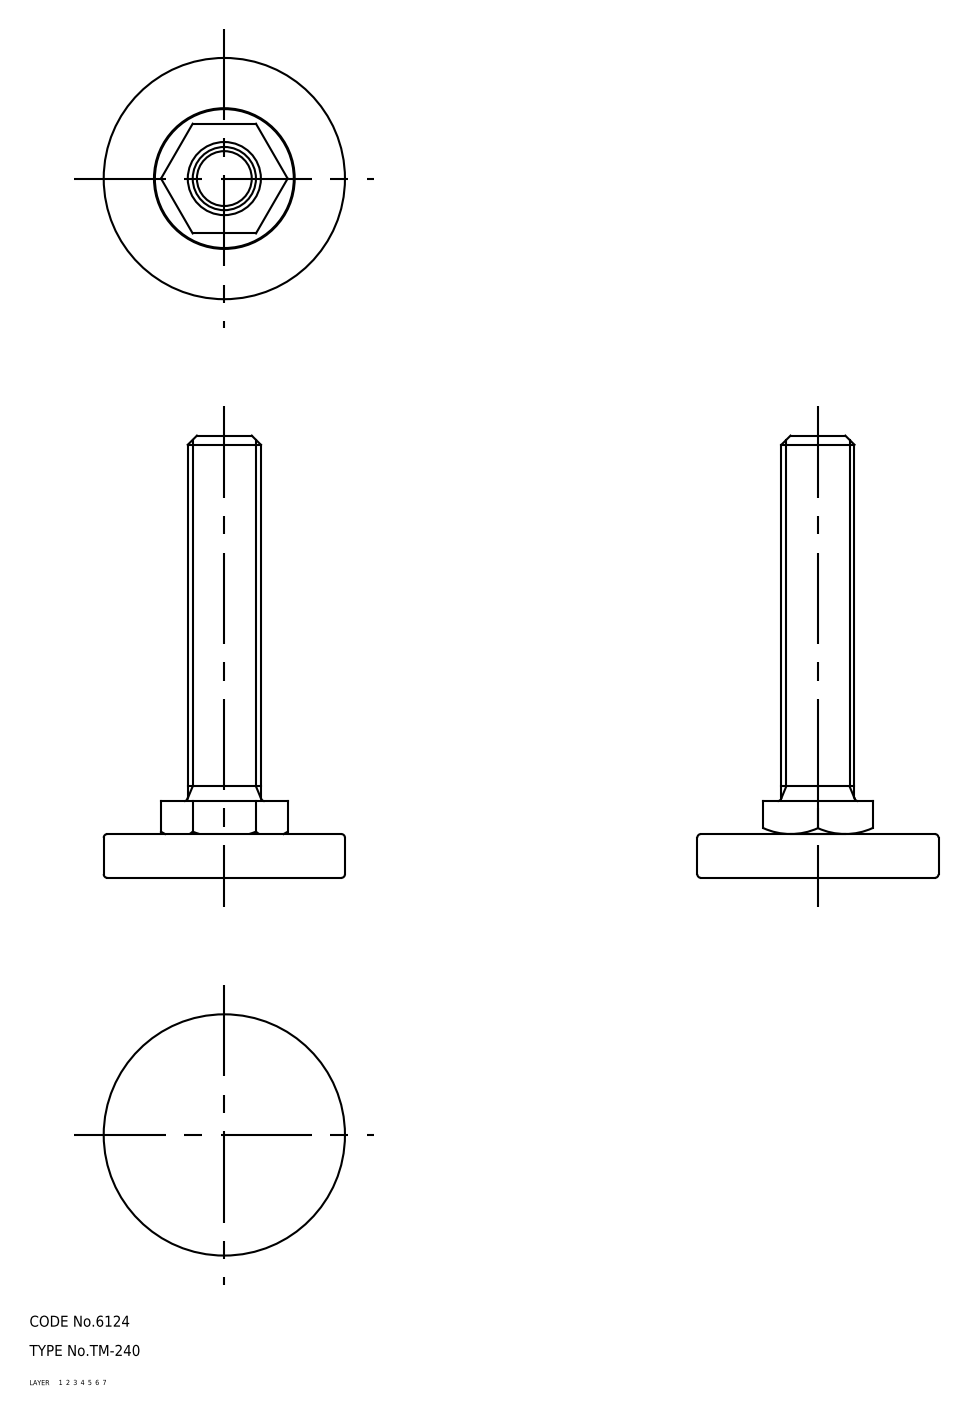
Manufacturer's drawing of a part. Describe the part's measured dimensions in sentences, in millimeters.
The part is named "washer; rubber pad; bolt; TM_240_8649_36". Its 3-D file was written by "CADfix (AUTOMOTIVE_DESIGN)". It is 3 solids with 43 faces: 0 planar, 0 cylindrical and 43 other. Overall it measures 121 by 66 by 66 millimeters. Its volume is 78 446 cubic millimeters and its surface area 20 037 square millimeters.
